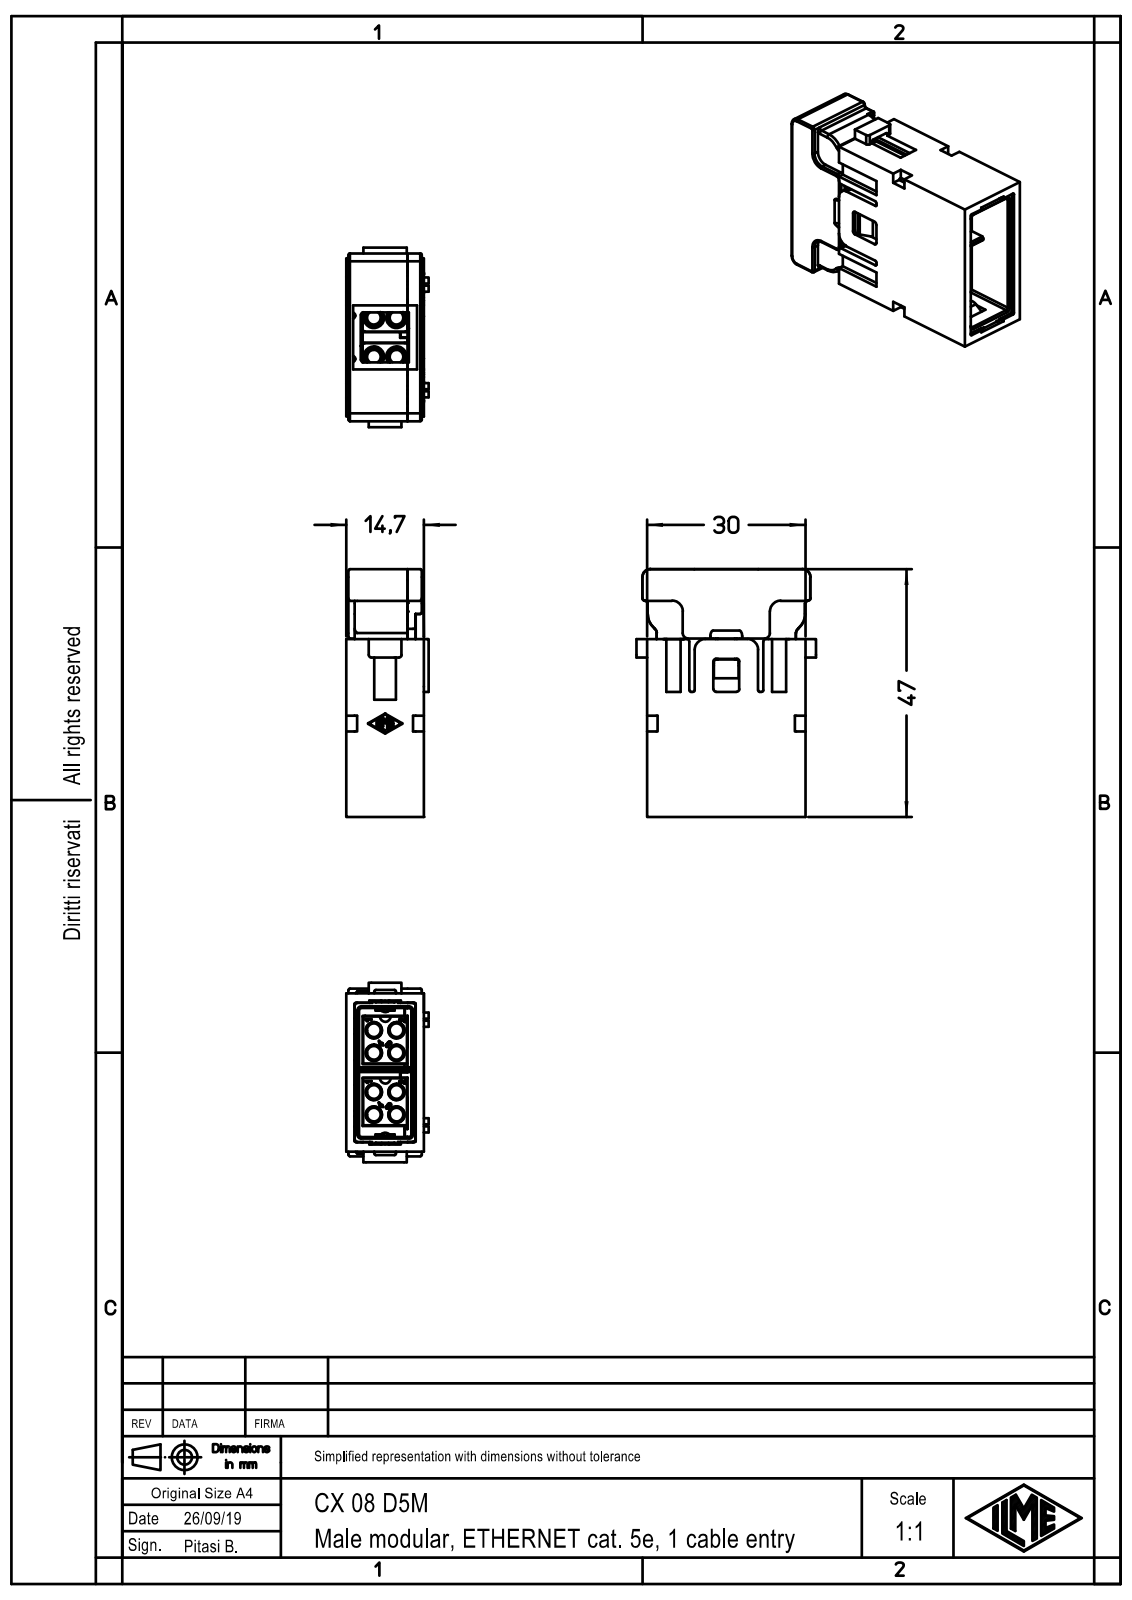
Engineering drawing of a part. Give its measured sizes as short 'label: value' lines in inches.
name: CX 08 D5M
written by: Creo Elements/Direct Modeling 20.1B 02-Apr-2019 (C) Parametric Technology GmbH (AUTOMOTIVE_DESIGN)
unit: in
bodies: 1 solid, 649 faces (377 planar, 203 cylindrical, 69 other)
size: 1.848 × 1.339 × 0.614
volume: 0.969 in³; area: 19.34 in²
holes: 10× ⌀0.102, 2× ⌀0.089, 2× ⌀0.197, 1× ⌀0.055
bosses: 2× ⌀0.185, 2× ⌀0.075, 1× ⌀0.051
rounds: 46× R0.02, 40× R0.012, 8× R0.016, 8× R0.039, 6× R0.079, 4× R0.004, 4× R0.008, 4× R0.026
face distances: 0.063, 0.516, 0.061, 0.518, 0.455, 0.453, 0.457, 0.579, 0.016, 0.045
hole spacings: 0.169, 0.239, 0.461, 0.491, 0.291, 0.337, 0.63, 0.652
